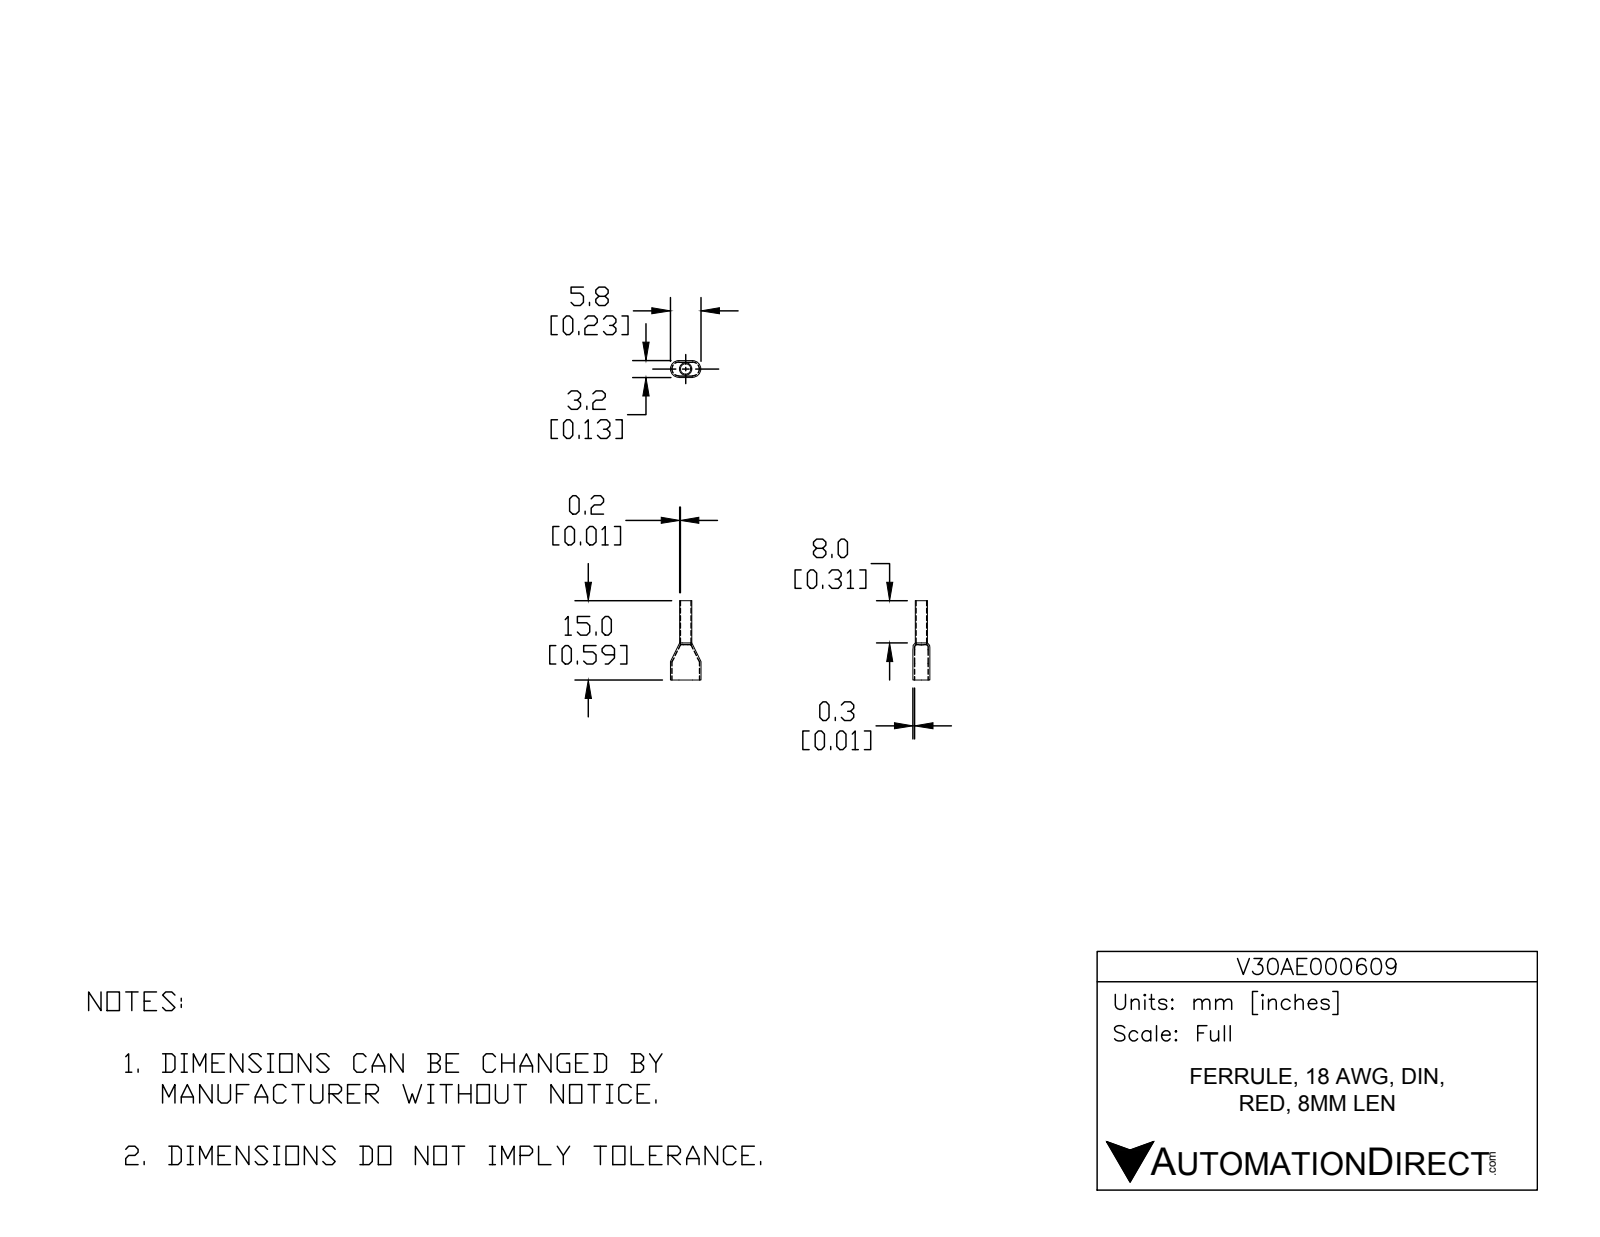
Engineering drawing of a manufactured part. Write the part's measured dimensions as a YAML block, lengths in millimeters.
part_name: "V30AE000609"
step_written_by: "SolidWorks 2017 (AUTOMOTIVE_DESIGN)"
units: millimeters
bodies: {solids: 2, faces: 36, planar: 14, cylindrical: 22, other: 0}
overall_size: [15, 5.8, 3.2]
volume: 35
surface_area: 294
round_holes:
  - {diameter: 2, count: 1}
round_bosses_or_shafts:
  - {diameter: 2.3, count: 1}
partial_cylinders:
  - {radius: 1.3, count: 4}
  - {radius: 1.6, count: 4}
face_to_face_distances: [2.9, 2.6, 3.2, 7, 15, 8, 6.7, 8.3]
